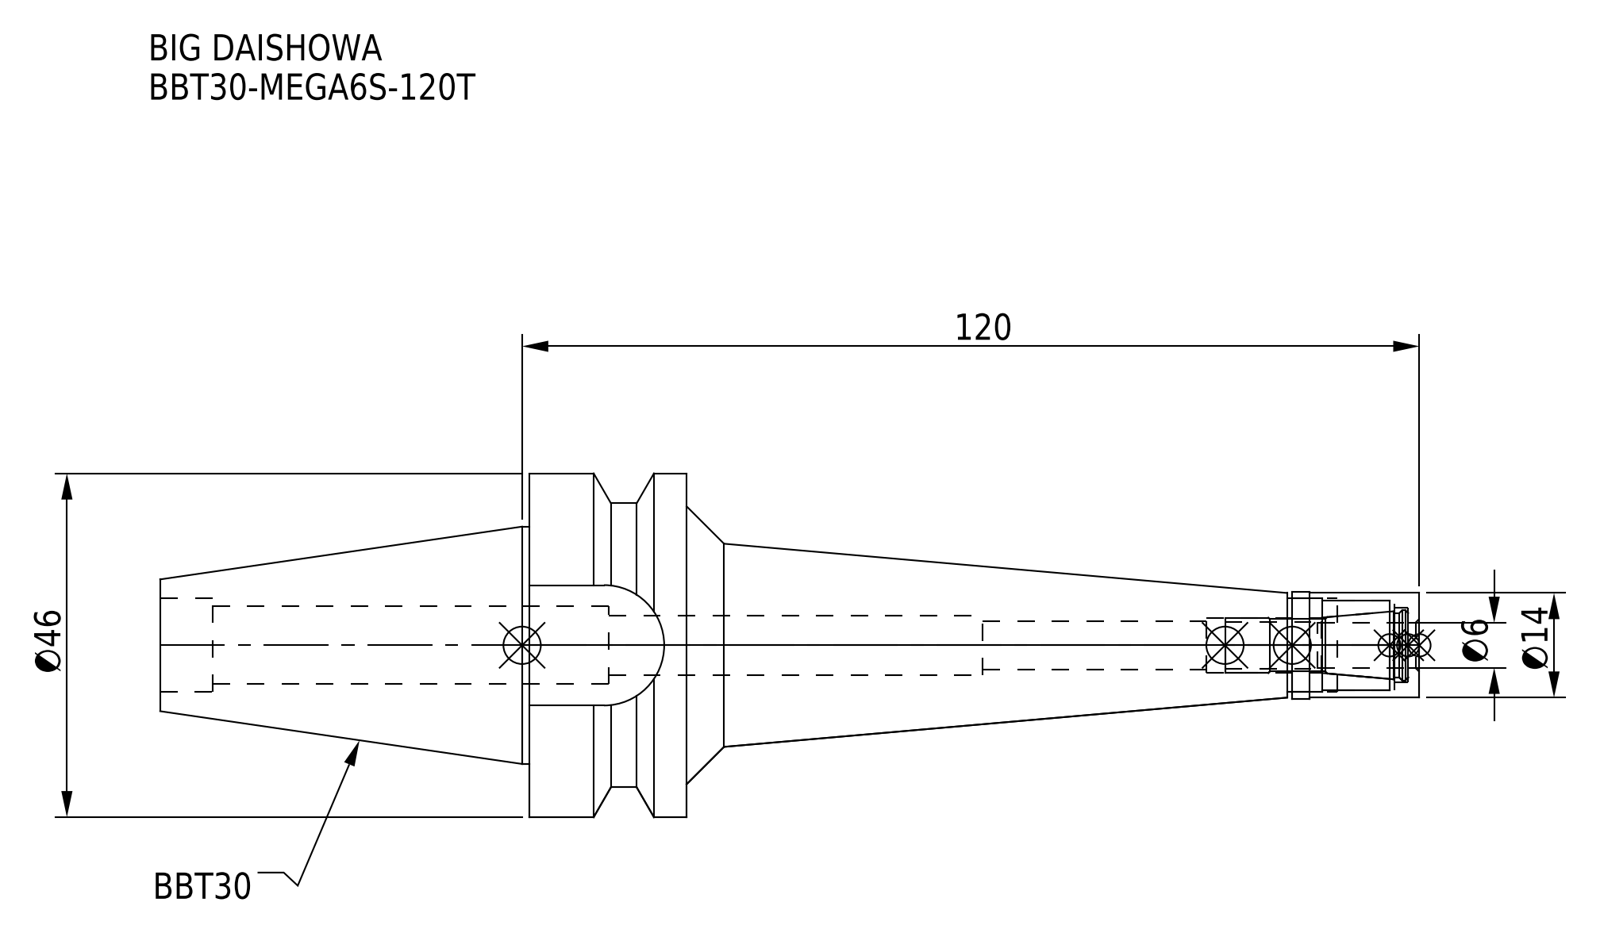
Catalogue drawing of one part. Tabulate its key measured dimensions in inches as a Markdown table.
| quantity | value |
| --- | --- |
| part name | BBT30-MEGA6S-120T-FreeParts; BBT30MS06120T-060_ASM.stp; BBT30-MEGA6S-120T_1.stp; BBT30-MEGA6S-120T.stp (+3 more) |
| STEP written by | SolidWorks 2019 (CONFIG_CONTROL_DESIGN) |
| units | inches |
| bodies | 2 solids, 74 faces (22 planar, 38 cylindrical, 14 other) |
| overall size | 6.63 × 1.811 × 1.811 |
| volume | 4.656 in³ |
| surface area | 33.2 in² |
| round holes (diameter × count) | 0.24 × 1, 0.252 × 1, 0.291 × 1, 0.315 × 1, 0.394 × 1, 0.409 × 1, 0.472 × 1, 0.492 × 1 |
| round bosses / shafts (diameter × count) | 1.811 × 1, 1.25 × 1, 0.563 × 1, 0.551 × 1 |
| partial cylindrical surfaces (radius × count) | 0.317 × 1, 0.748 × 1 |
| main face-to-face distances | 0.827, 1.283, 2.772, 1.945, 3.858, 4.685, 6.63, 0.634, 0.028, 0.539 |
